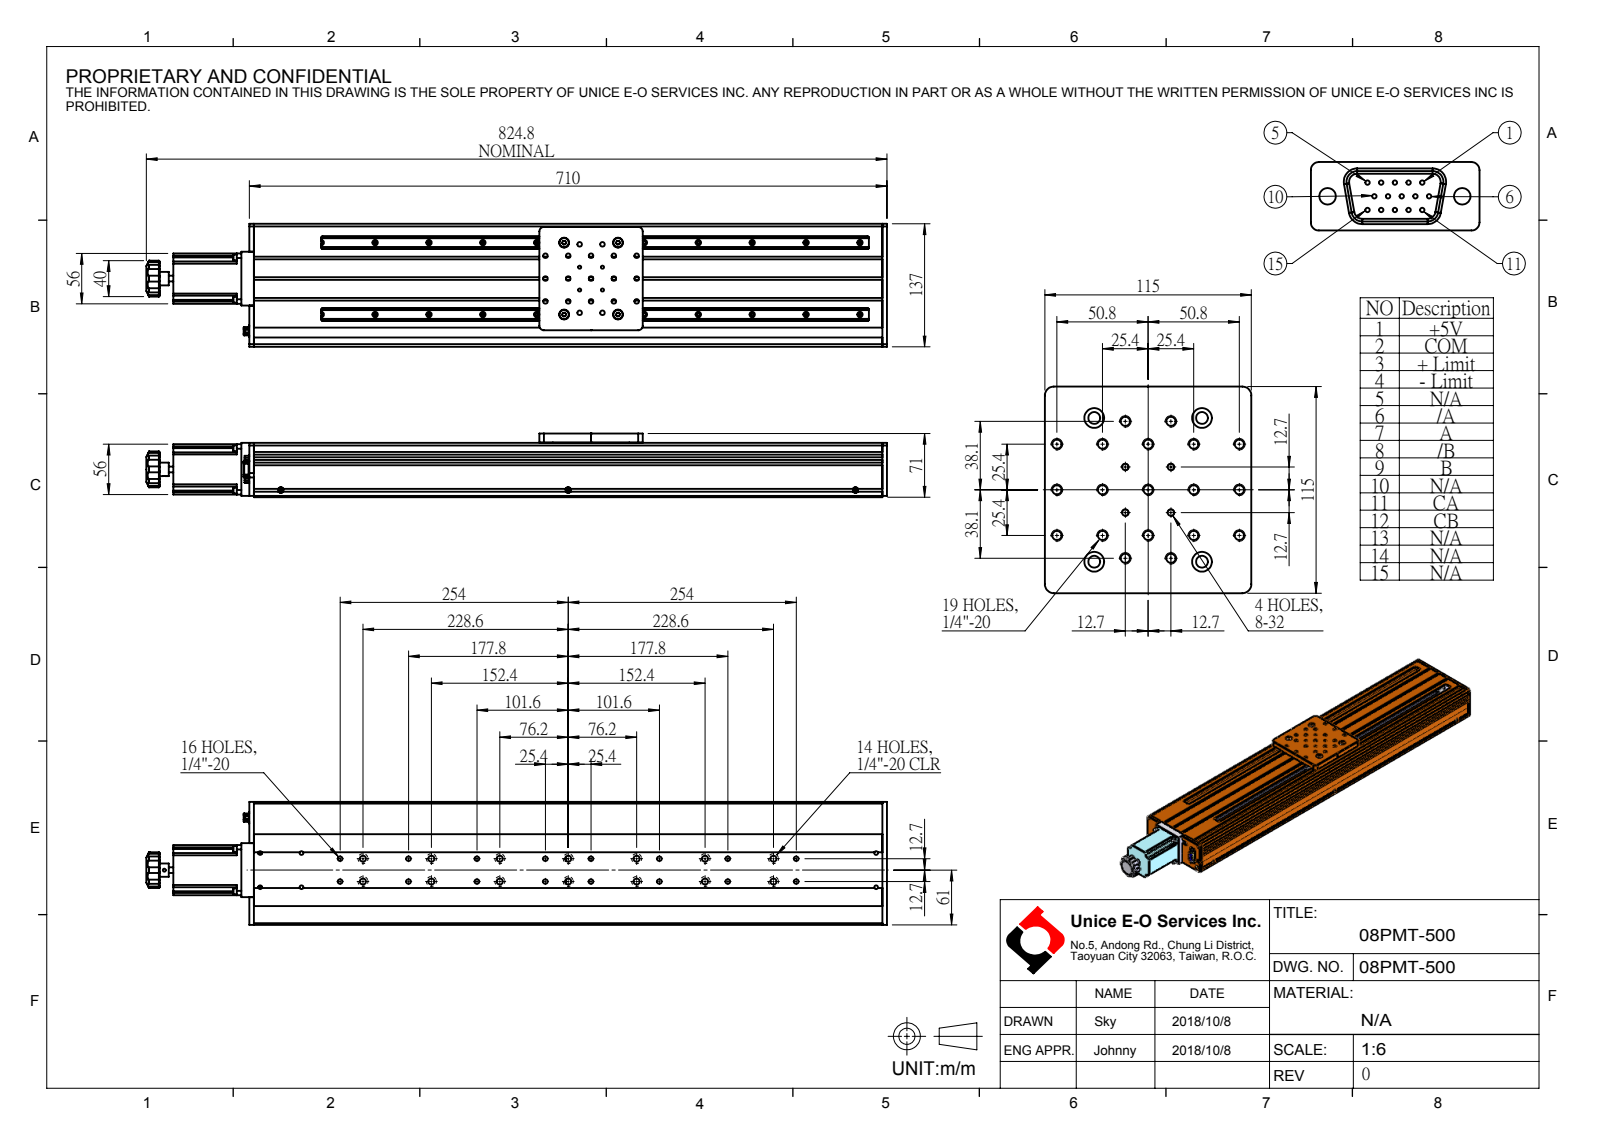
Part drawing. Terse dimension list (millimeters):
name: 08PMT-500
written by: SolidWorks 2016 (AUTOMOTIVE_DESIGN)
unit: mm
bodies: 0 solids, 732 faces (341 planar, 283 cylindrical, 108 other)
size: 824.8 × 137 × 71
holes: 35× ⌀5.11, 14× ⌀6.76, 14× ⌀11.11, 6× ⌀4.2, 4× ⌀1, 4× ⌀3.45, 4× ⌀11, 3× ⌀0.8, 2× ⌀2, 2× ⌀2.5, 1× ⌀22, 1× ⌀25.5
bosses: 4× ⌀6.5, 2× ⌀7.7, 2× ⌀5.8, 2× ⌀3, 1× ⌀16, 1× ⌀15, 1× ⌀6.35
rounds: 10× R1.5, 8× R4, 8× R5, 8× R7.41, 4× R2, 4× R4.5, 3× R0.5, 3× R3
face distances: 2, 60.5, 135, 133, 10.5, 1.5, 59, 137, 1.7, 9
hole spacings: 25.4, 76.2, 80.32, 152.4, 154.5, 101.6, 104.73, 177.8
